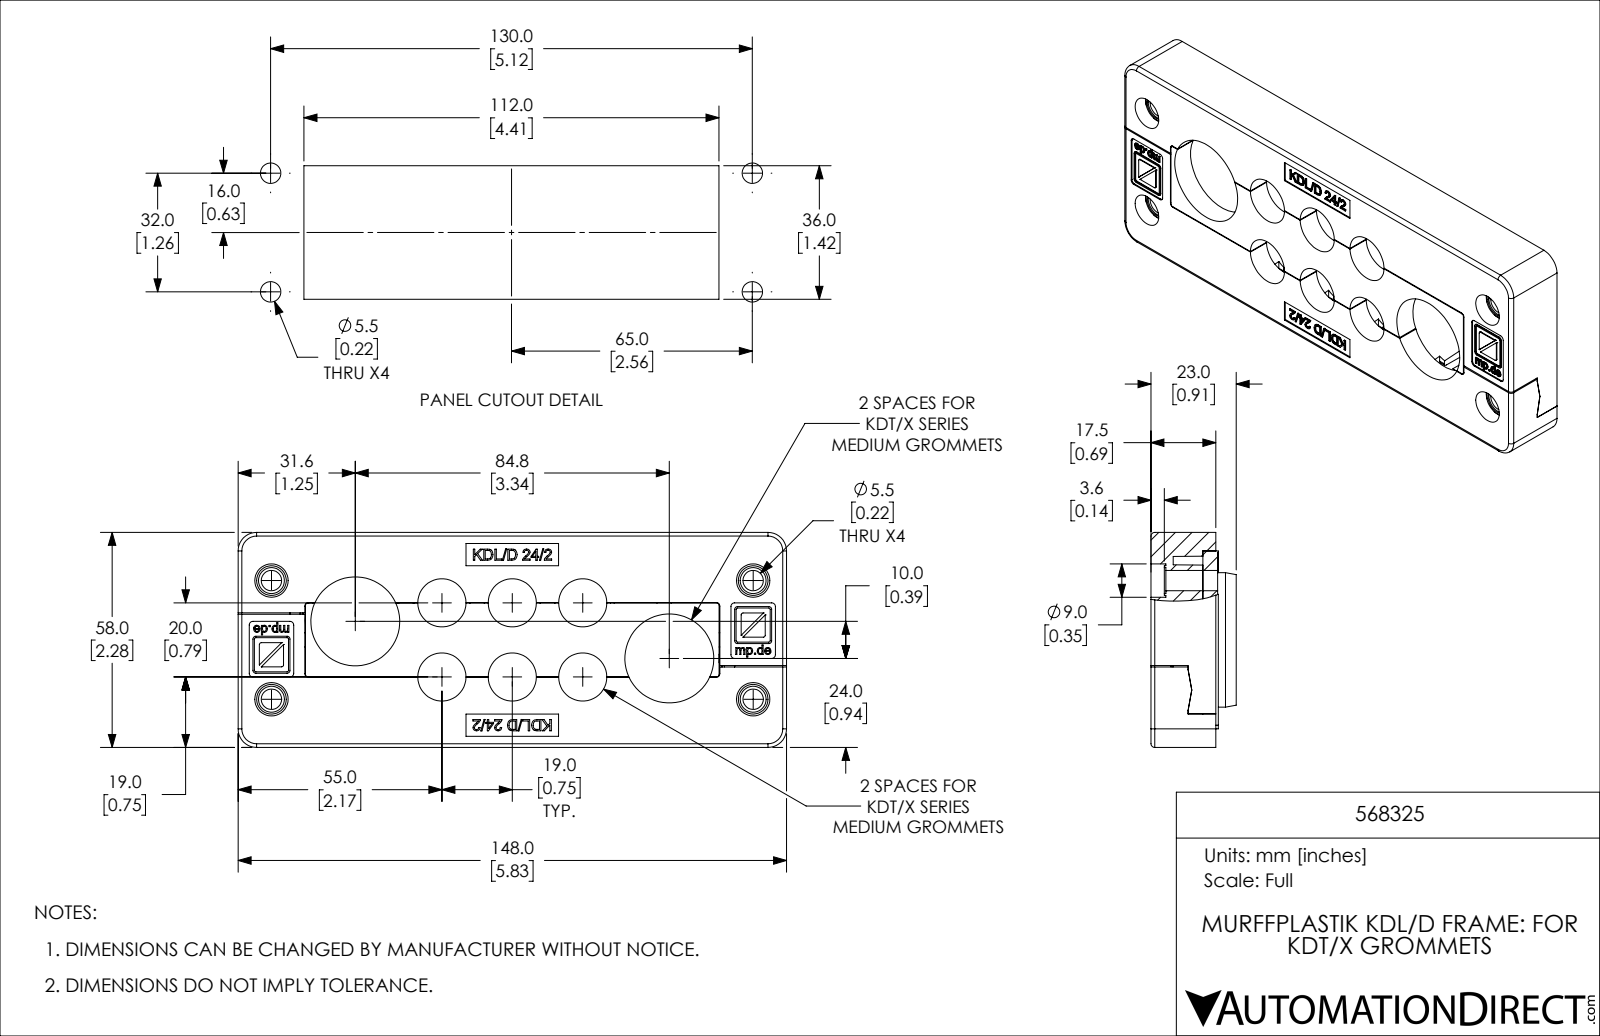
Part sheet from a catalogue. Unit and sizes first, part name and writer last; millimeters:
Units: millimetres
Overall size (bounding box): 148 × 58 × 23
Round holes (diameter × count): ⌀5 ×6, ⌀13 ×6, ⌀15 ×6, ⌀5.5 ×4, ⌀7 ×4, ⌀9 ×4, ⌀6 ×2, ⌀24.9 ×2, ⌀24 ×1
Round bosses / shafts (diameter × count): ⌀8 ×4
Partial cylindrical surfaces — rounded edges, fillets, slot ends (radius × count): R1 ×36, R0.5 ×28, R0.4 ×12, R0.8 ×8, R7.5 ×6, R0.1 ×4, R0.2 ×4, R0.3 ×4
Main face-to-face distances: 5, 4, 6, 53, 14, 0.5, 3.5, 18, 58, 11.5
Hole centre spacings: 19, 11.3, 16.9, 22, 27.6, 46.4, 52.8, 65.3
Volume: 111 100 mm³ · Surface area: 58 560 mm²
Bodies: 4 solids, 1530 faces (896 planar, 269 cylindrical, 365 other)
Part name (STEP PRODUCT): 568325
STEP written by: SolidWorks 2019 (CONFIG_CONTROL_DESIGN)
